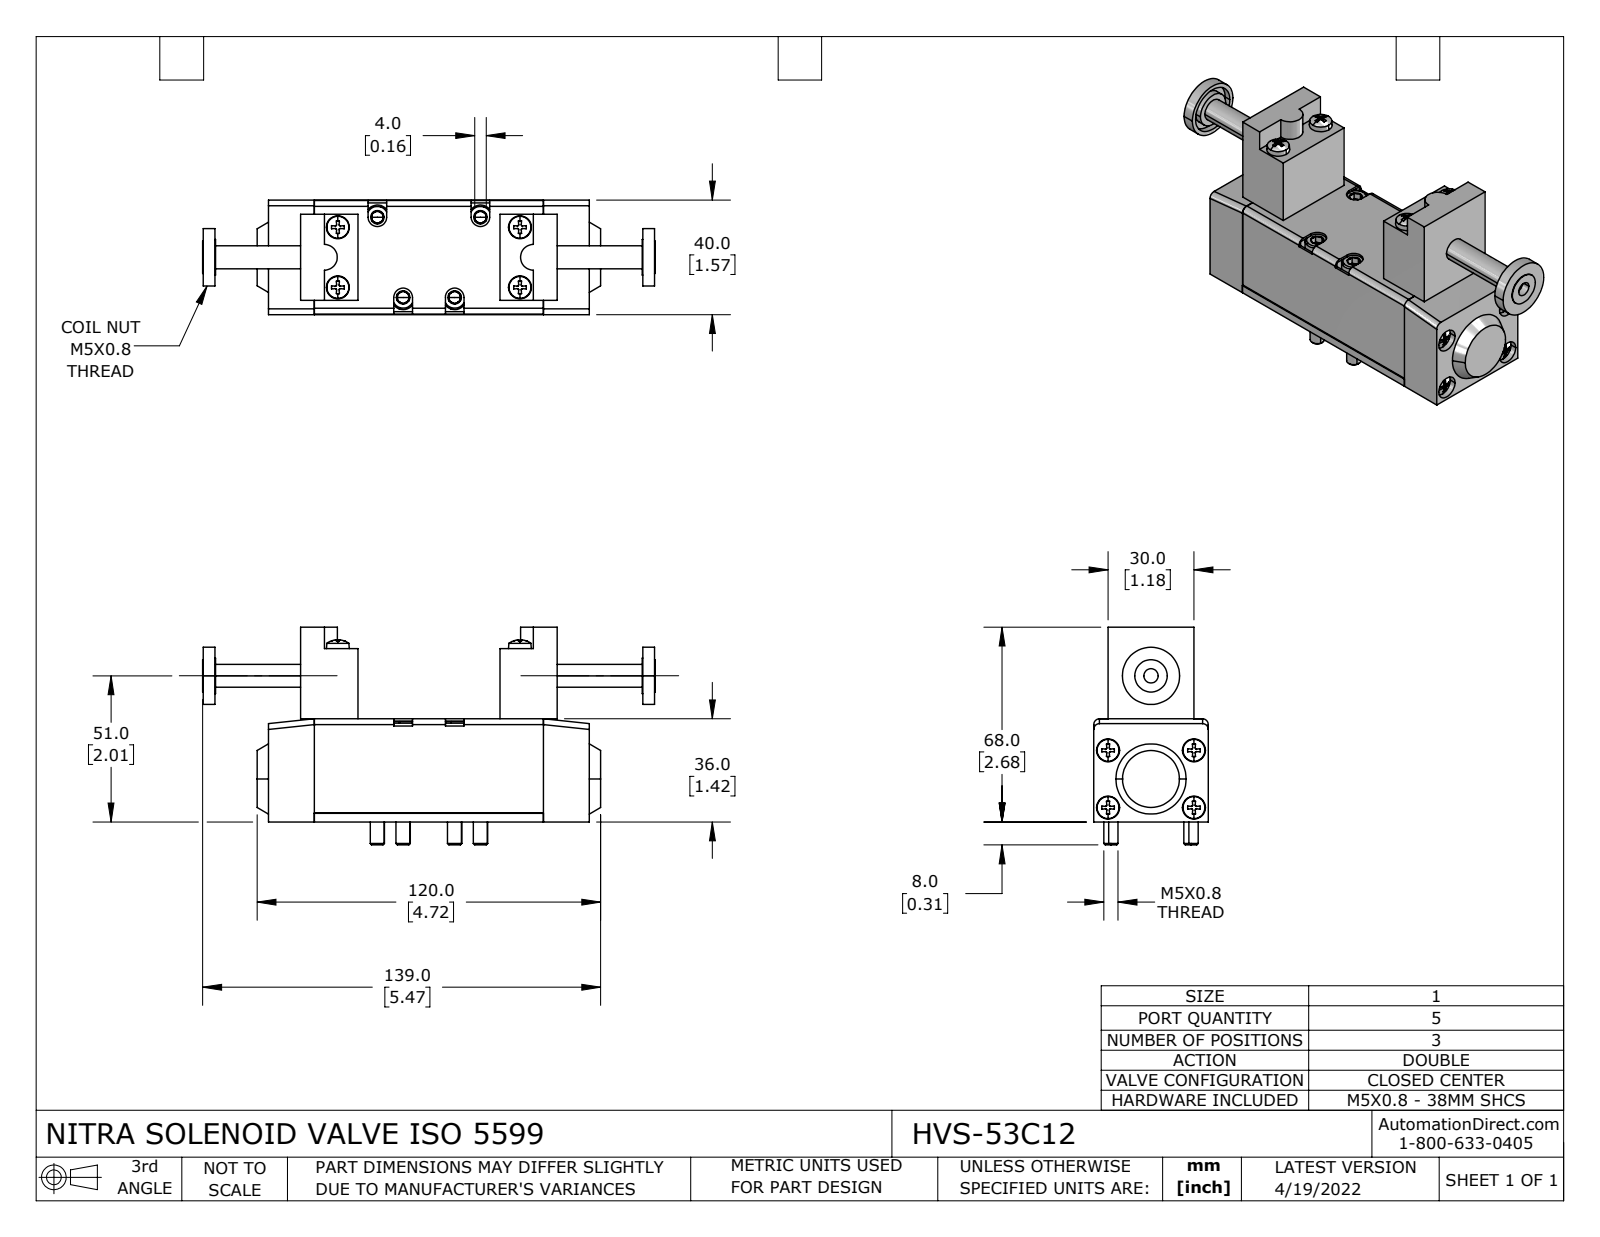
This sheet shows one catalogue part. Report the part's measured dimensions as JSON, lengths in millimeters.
{"part_name": "HVS-53C12", "step_written_by": "SolidWorks 2021 (CONFIG_CONTROL_DESIGN)", "units": "millimeters", "bodies": {"solids": 21, "faces": 850, "planar": 434, "cylindrical": 156, "other": 260}, "overall_size": [158, 76, 40], "volume_mm3": 199600, "surface_area_mm2": 54310, "round_holes": [[3.3, 8], [4.1, 4], [5.5, 4], [8, 4], [5, 1], [16.9, 1]], "round_bosses_or_shafts": [[4, 8], [8.5, 4], [5, 4], [20, 1], [12.4, 1], [11.3, 1], [8, 1]], "partial_cylinders_radius": [[2, 6], [3.3, 4], [5, 4], [4.5, 2]], "face_to_face_distances": [4.8, 36, 80, 39.8, 39.6, 84.8, 5, 35, 34.8, 20], "hole_center_spacings": [14.2, 20, 21, 23.1, 28.1, 29.4, 30, 30]}
